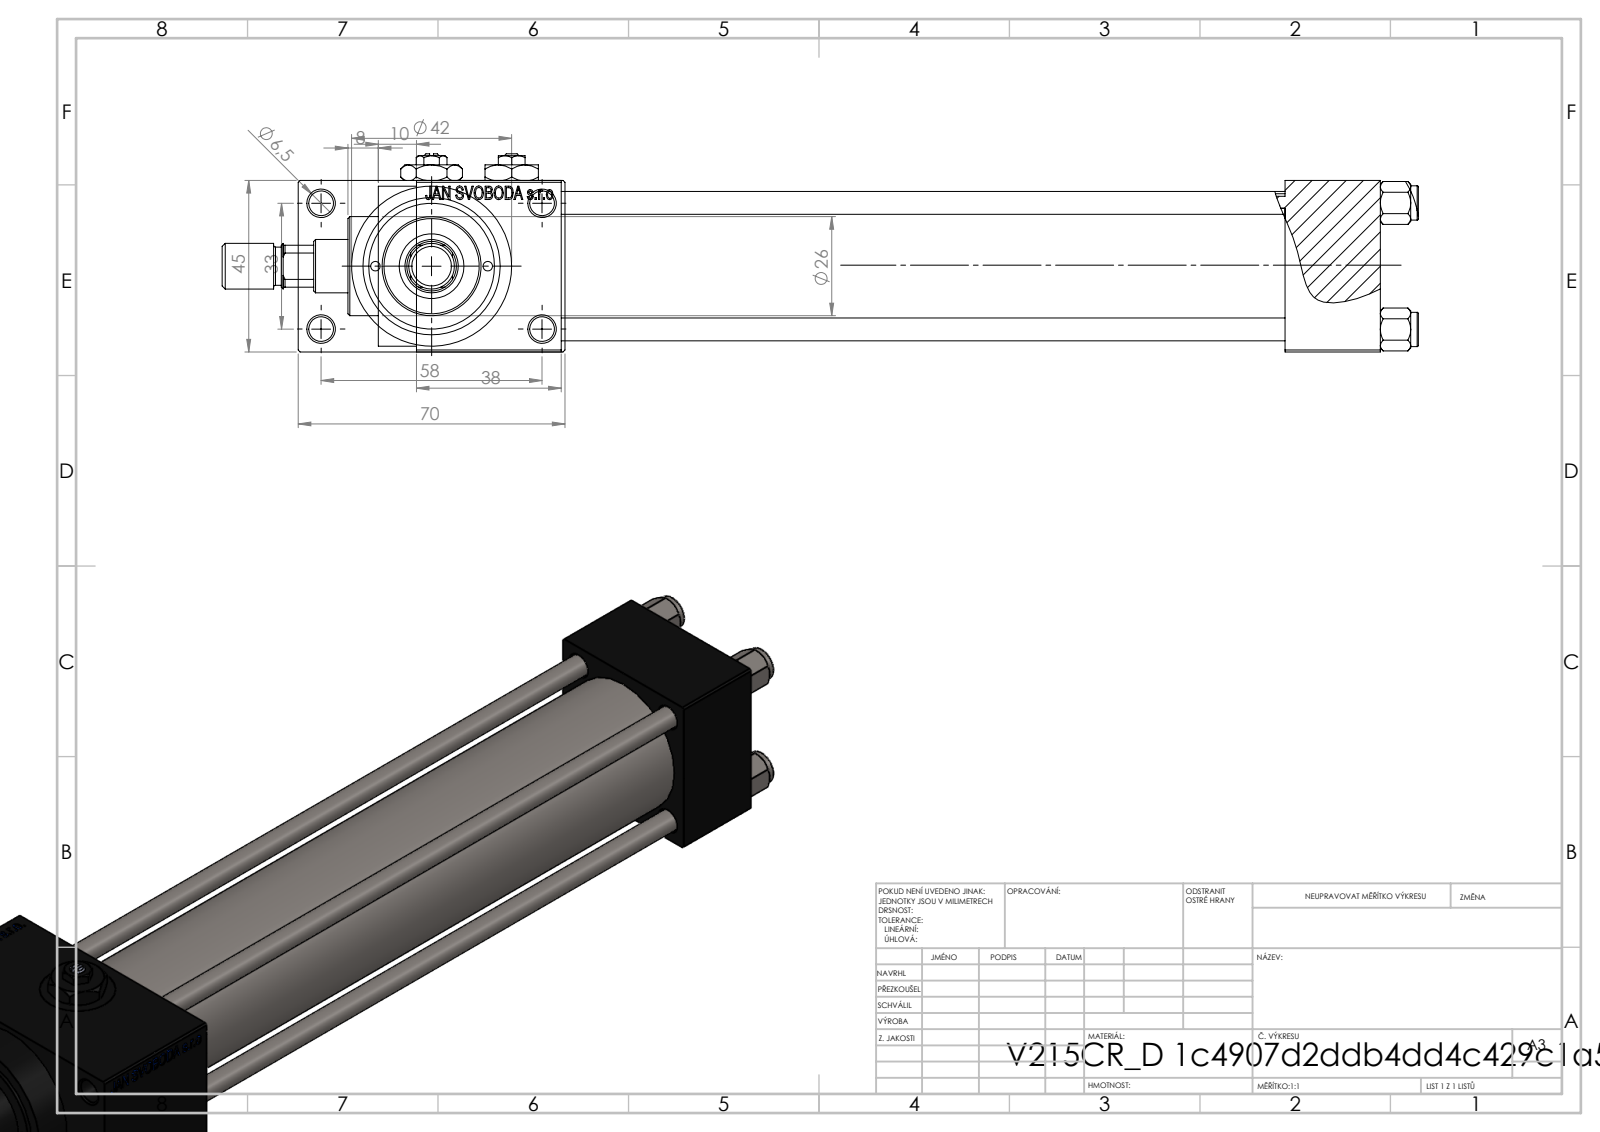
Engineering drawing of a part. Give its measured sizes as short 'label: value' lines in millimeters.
name: NUT_M5_D; V215CR_D_TYCINKA; V215_VC_A; ROD_END_AH (+3 more)
written by: SolidWorks 2019 (CONFIG_CONTROL_DESIGN)
unit: mm
bodies: 13 solids, 1171 faces (525 planar, 100 cylindrical, 546 other)
size: 314 × 70 × 52
volume: 315 373 mm³; area: 124 330 mm²
holes: 5× ⌀6.5, 4× ⌀6, 3× ⌀13.16, 3× ⌀20, 2× ⌀2.5, 2× ⌀7, 1× ⌀14, 1× ⌀17, 1× ⌀24, 1× ⌀32, 1× ⌀33
bosses: 4× ⌀9, 1× ⌀42, 1× ⌀38, 1× ⌀26, 1× ⌀12, 1× ⌀10
rounds: 1× R6.5
face distances: 45, 25, 12.5, 190, 215, 57.5, 228, 38, 253, 70
hole spacings: 12.4, 16.7, 21.8, 23.48, 33.2, 33.37, 35.35, 35.47
